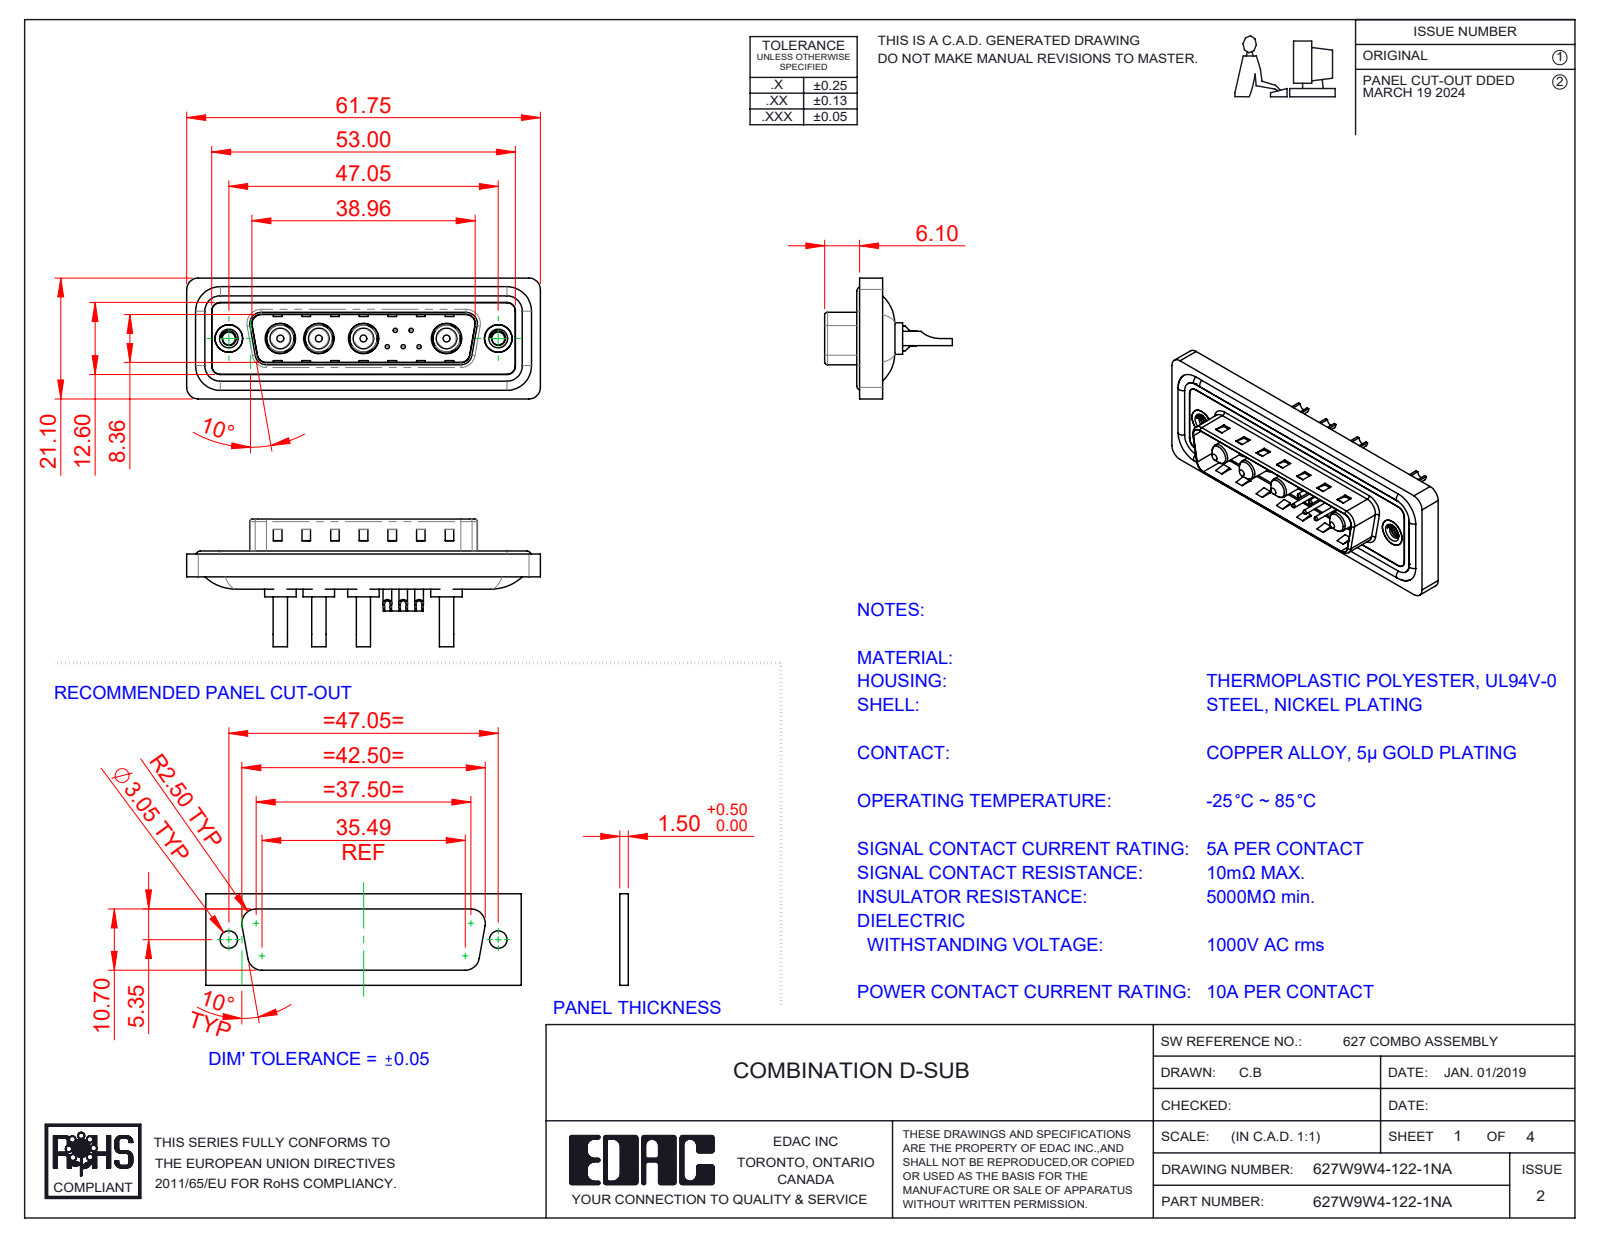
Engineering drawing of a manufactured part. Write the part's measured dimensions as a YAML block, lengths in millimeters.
part_name: "627Combo Shell Front_25 Contacts; 627Combo Contact Row 2_22; Power Pin_10A SC; 627W9W4-122-1NA (+5 more)"
step_written_by: "SolidWorks 2023 (CONFIG_CONTROL_DESIGN)"
units: millimeters
bodies: {solids: 20, faces: 842, planar: 302, cylindrical: 358, other: 182}
overall_size: [61.75, 22.3, 21.1]
volume: 7402
surface_area: 12064
round_holes:
  - {diameter: 0.75, count: 5}
  - {diameter: 1, count: 5}
  - {diameter: 1.6, count: 5}
  - {diameter: 2, count: 5}
  - {diameter: 1.7, count: 4}
  - {diameter: 4.85, count: 4}
  - {diameter: 5.3, count: 4}
  - {diameter: 2.26, count: 2}
  - {diameter: 4, count: 2}
  - {diameter: 4.8, count: 2}
  - {diameter: 5, count: 2}
round_bosses_or_shafts:
  - {diameter: 1.5, count: 5}
  - {diameter: 5.5, count: 4}
  - {diameter: 5.2, count: 4}
  - {diameter: 4.75, count: 4}
  - {diameter: 3.75, count: 4}
  - {diameter: 3.6, count: 4}
  - {diameter: 2.5, count: 4}
  - {diameter: 1.6, count: 4}
partial_cylinders:
  - {radius: 1.5, count: 22}
  - {radius: 2, count: 18}
  - {radius: 0.5, count: 8}
  - {radius: 1.6, count: 8}
  - {radius: 1, count: 6}
  - {radius: 0.25, count: 4}
  - {radius: 0.6, count: 4}
  - {radius: 0.65, count: 4}
face_to_face_distances: [0.4, 1.5, 1.1, 0.5, 1.6, 3.1, 2.9, 0.82, 9.58, 5.65]
hole_center_spacings: [3.16, 2.77, 5.04, 14.51, 2.78, 4.4, 4.41, 5]
